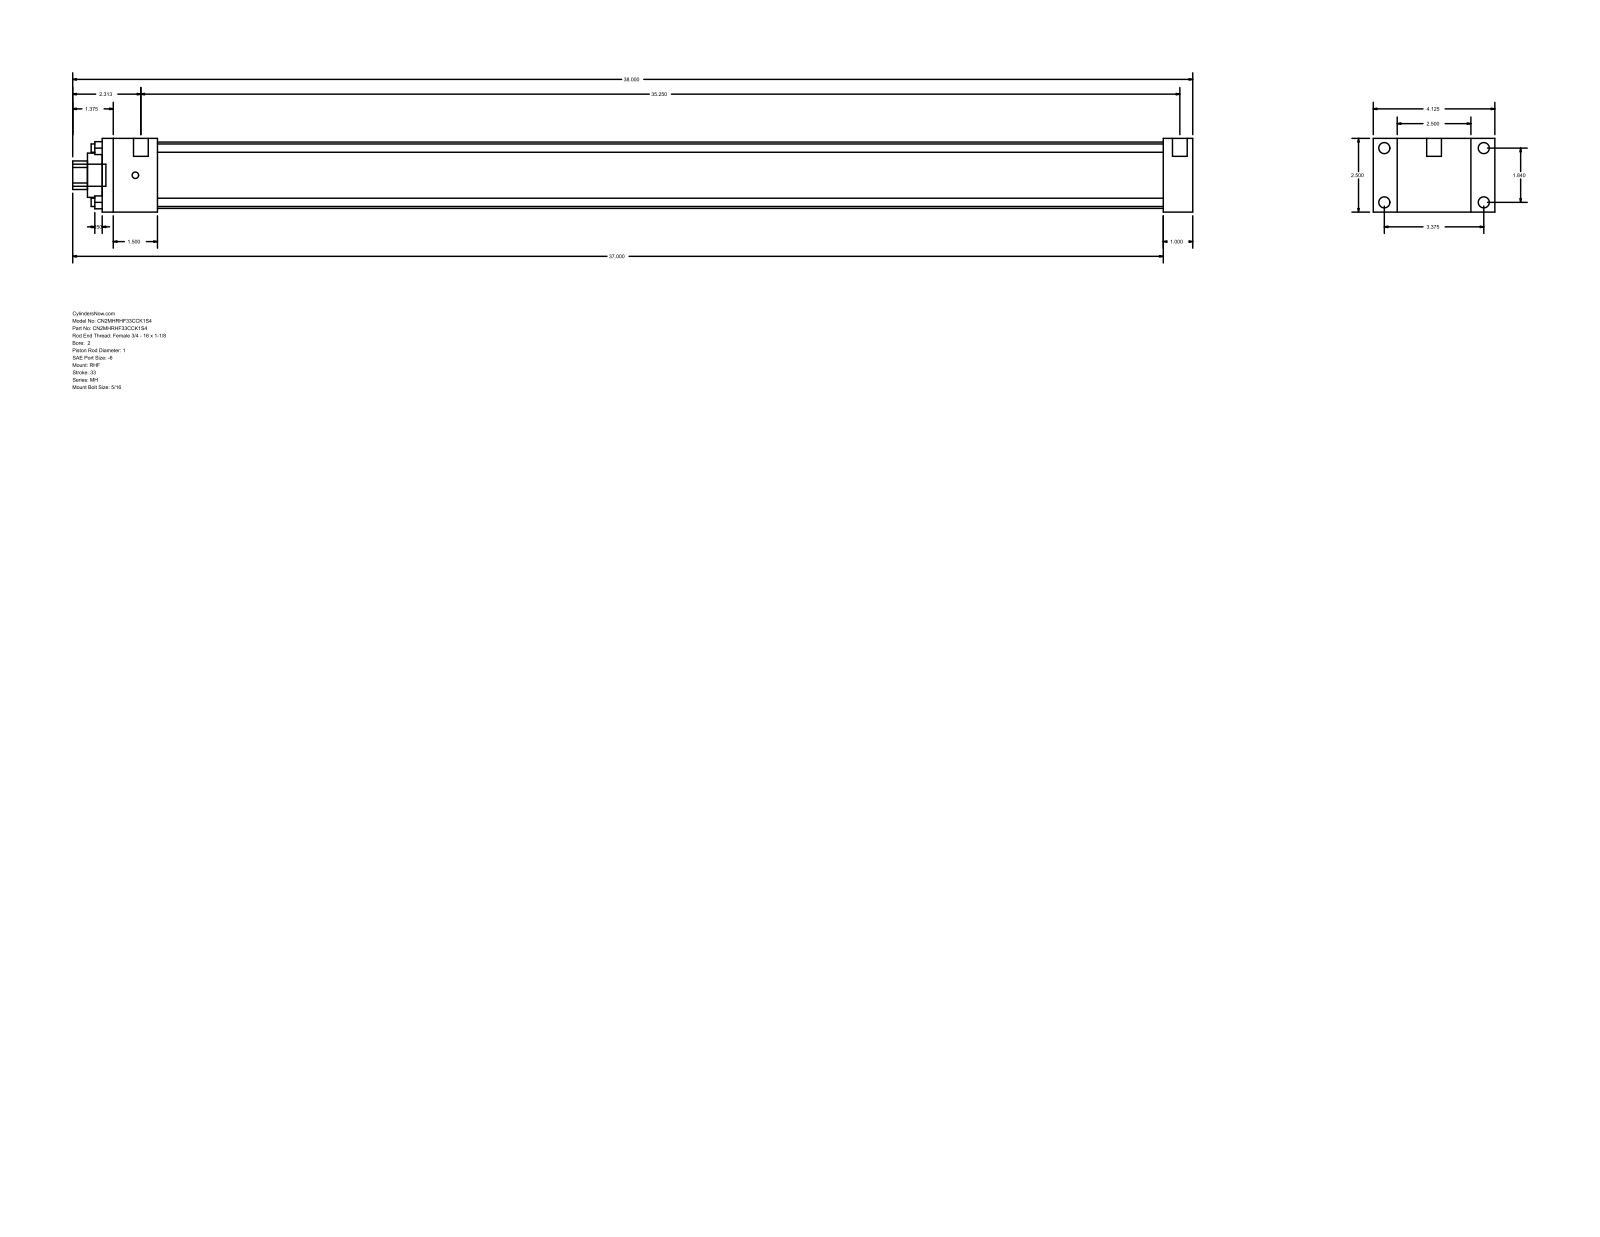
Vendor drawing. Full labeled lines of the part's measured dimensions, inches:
Part name (STEP PRODUCT): MH_RHF__0200_1
STEP written by: GSSL Pune (CONFIG_CONTROL_DESIGN)
Units: inches
Bodies: 0 solids, 88 faces (60 planar, 28 cylindrical, 0 other)
Overall size (bounding box): 38 × 4.125 × 2.5
Round holes (diameter × count): ⌀0.281 ×4, ⌀1 ×1, ⌀1.5 ×1, ⌀2.25 ×1
Round bosses / shafts (diameter × count): ⌀0.375 ×4, ⌀0.219 ×4, ⌀0.5 ×2, ⌀0.75 ×1
Partial cylindrical surfaces — rounded edges, fillets, slot ends (radius × count): R0.484 ×1
Main face-to-face distances: 2.5, 1, 0.813, 3.313, 37, 36, 4.125, 1.875, 34.125, 35.125
Hole centre spacings: 1.301, 1.84, 2.602
